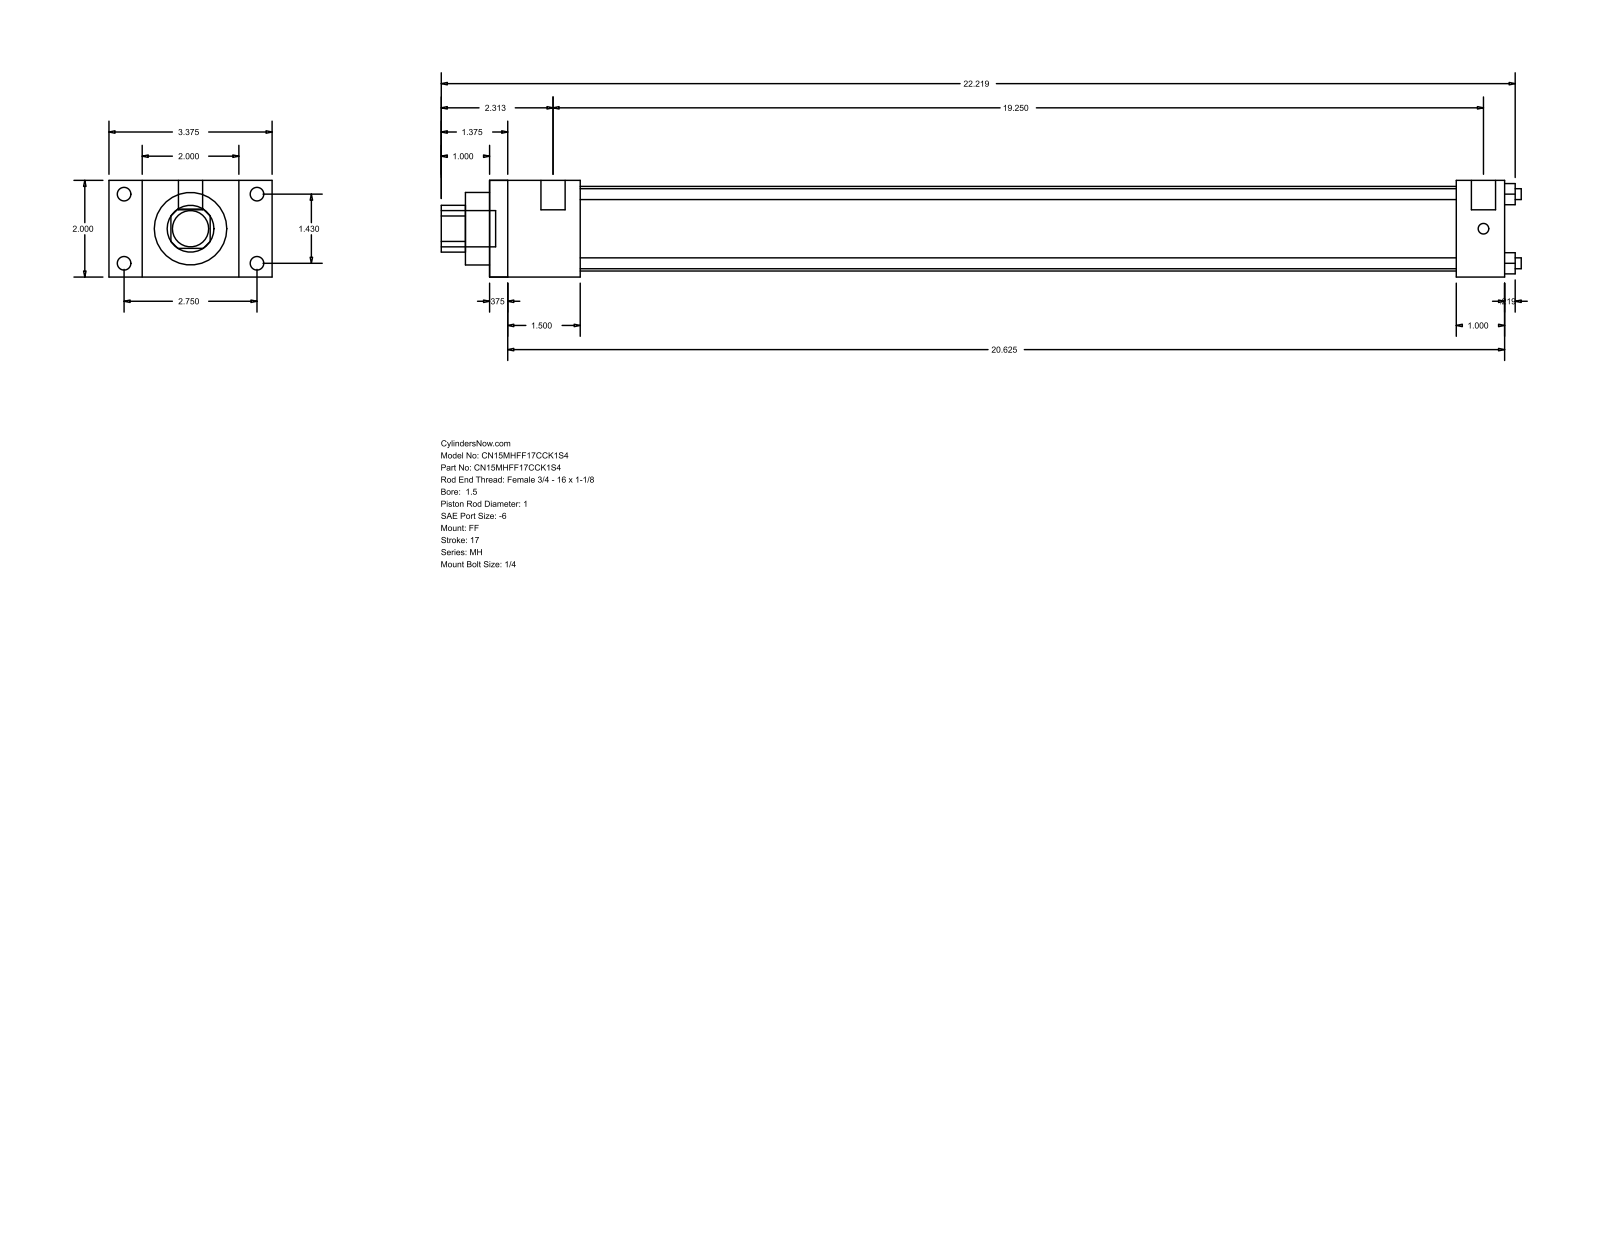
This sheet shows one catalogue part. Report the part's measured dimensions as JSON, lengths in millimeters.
{"part_name": "MH_FF__0150_1", "step_written_by": "GSSL Pune (CONFIG_CONTROL_DESIGN)", "units": "millimeters", "bodies": {"solids": 0, "faces": 92, "planar": 64, "cylindrical": 28, "other": 0}, "overall_size": [567.53, 85.72, 50.8], "round_holes": [[5.71, 4], [25.4, 1], [38.1, 1], [44.45, 1]], "round_bosses_or_shafts": [[7.14, 4], [5.56, 4], [12.7, 2], [19.05, 1]], "partial_cylinders_radius": [[12.29, 1]], "face_to_face_distances": [50.8, 533.4, 9.52, 523.88, 25.4, 17.46, 68.26, 47.63, 38.11, 485.77], "hole_center_spacings": [25.68, 36.32, 51.36]}
